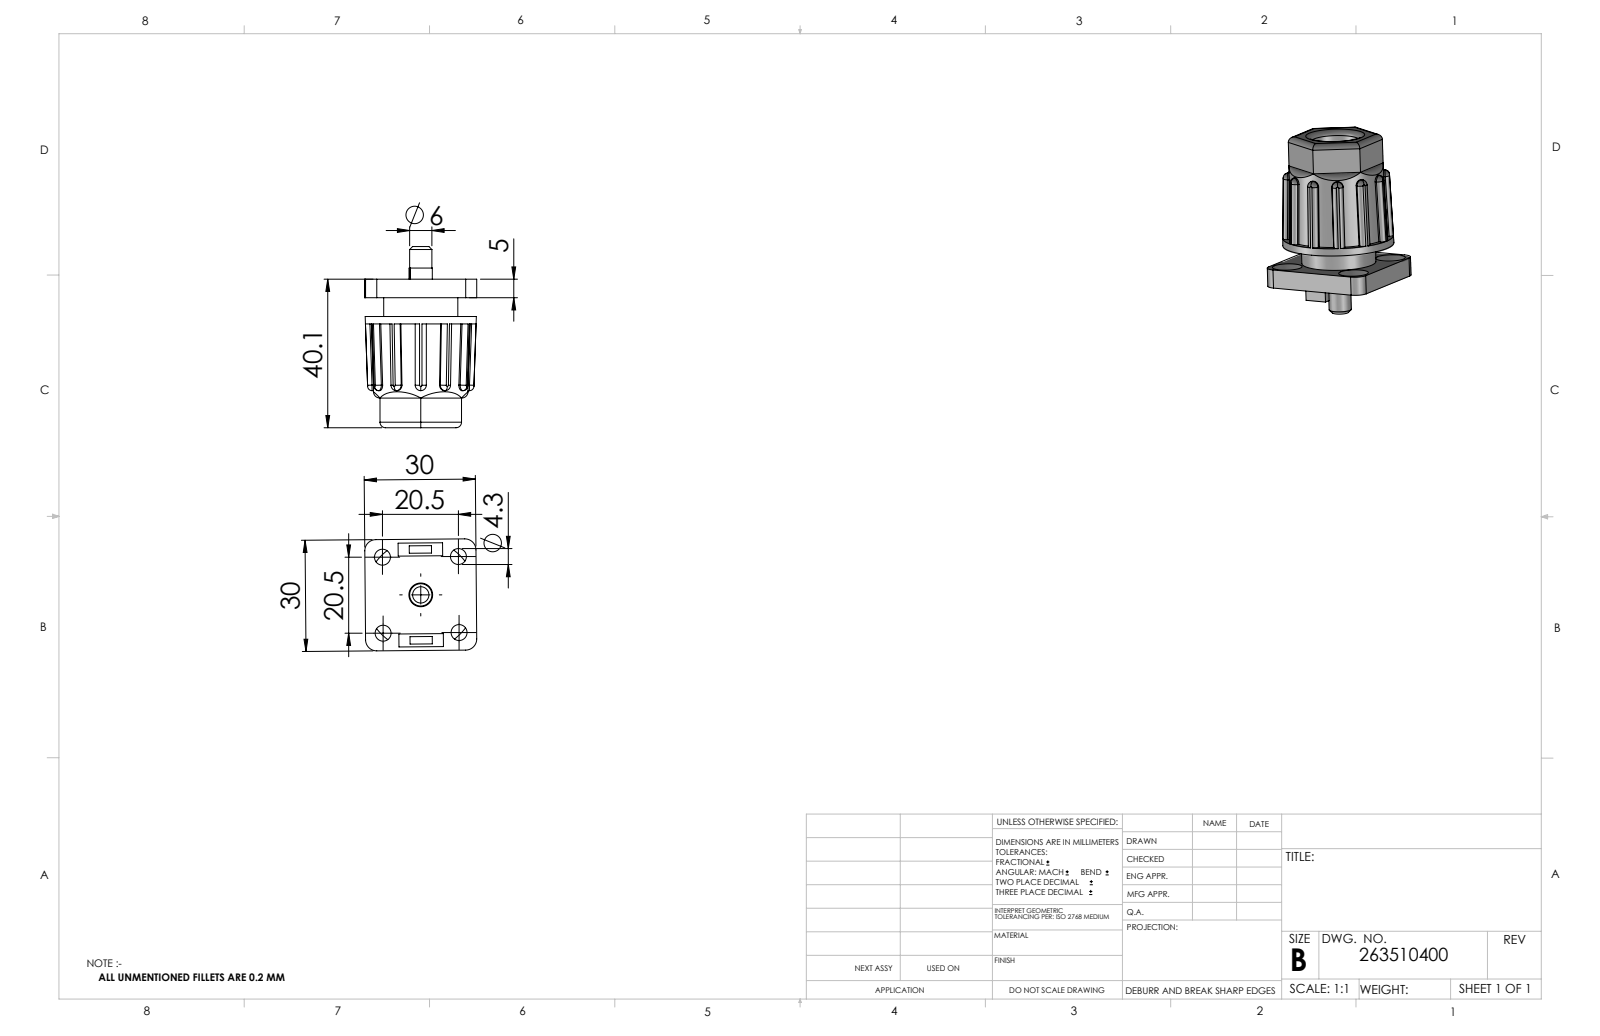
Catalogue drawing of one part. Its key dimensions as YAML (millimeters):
part_name: "263510400_c_1"
step_written_by: "SolidWorks 2014 (CONFIG_CONTROL_DESIGN)"
units: millimeters
bodies: {solids: 4, faces: 296, planar: 132, cylindrical: 61, other: 103}
overall_size: [48.87, 30.2, 30.2]
volume: 17214
surface_area: 14067
round_holes:
  - {diameter: 4.3, count: 4}
  - {diameter: 5, count: 1}
  - {diameter: 6, count: 1}
  - {diameter: 6.4, count: 1}
  - {diameter: 8.4, count: 1}
  - {diameter: 13, count: 1}
  - {diameter: 16.5, count: 1}
  - {diameter: 18, count: 1}
  - {diameter: 21.5, count: 1}
round_bosses_or_shafts:
  - {diameter: 20, count: 1}
  - {diameter: 15, count: 1}
  - {diameter: 10, count: 1}
partial_cylinders:
  - {radius: 1.5, count: 12}
  - {radius: 3, count: 4}
  - {radius: 0.75, count: 2}
face_to_face_distances: [5, 10.07, 5.07, 30, 22, 3, 18, 4, 7, 10]
hole_center_spacings: [14.5, 20.5, 28.99]
